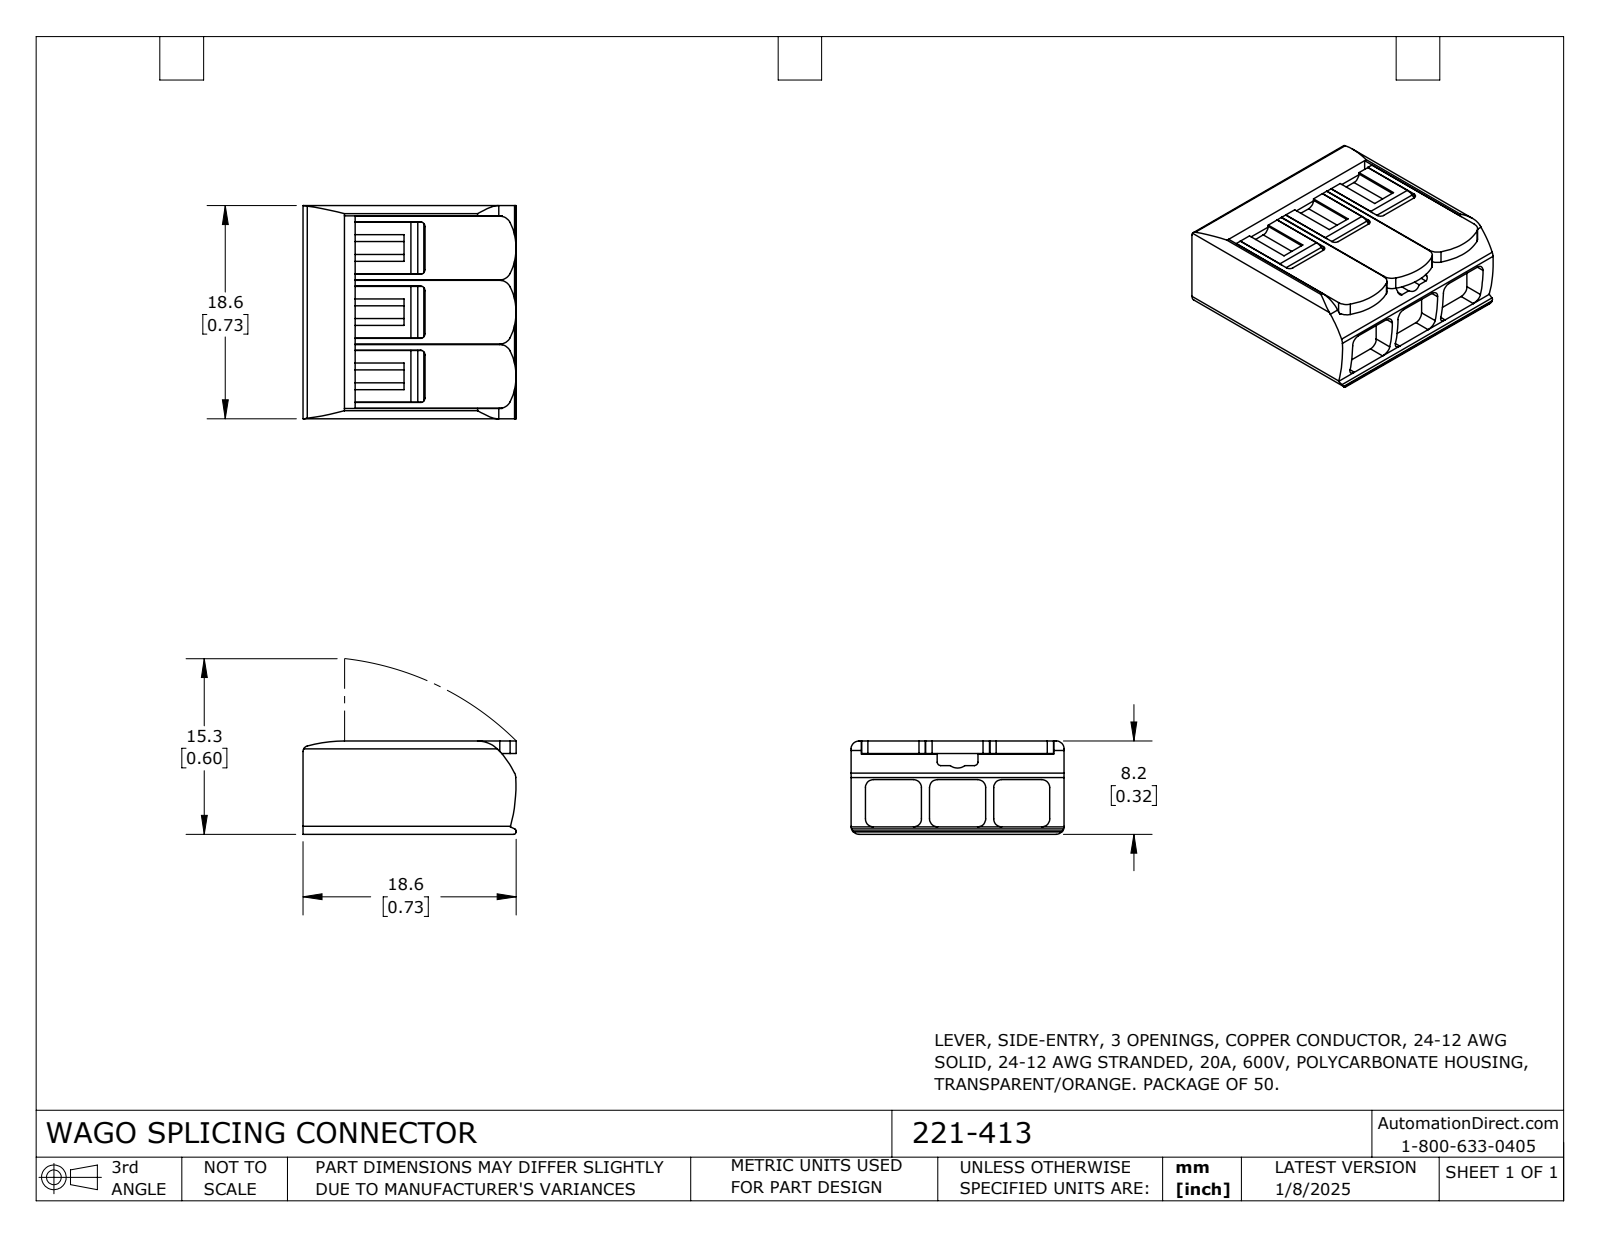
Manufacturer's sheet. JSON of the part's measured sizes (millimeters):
{"part_name": "221-413", "step_written_by": "SolidWorks 2023 (CONFIG_CONTROL_DESIGN)", "units": "millimeters", "bodies": {"solids": 1, "faces": 161, "planar": 96, "cylindrical": 65, "other": 0}, "overall_size": [18.6, 18.6, 8.15], "volume_mm3": 2578, "surface_area_mm2": 1738, "partial_cylinders_radius": [[0.7, 16], [1, 8], [0.3, 6], [0.4, 6], [0.6, 6], [0.2, 4], [5, 3], [0.5, 1]], "face_to_face_distances": [8.15, 18.6, 5.6, 16.6, 7.05, 1.1, 7, 1.15, 0.52, 11.2]}
